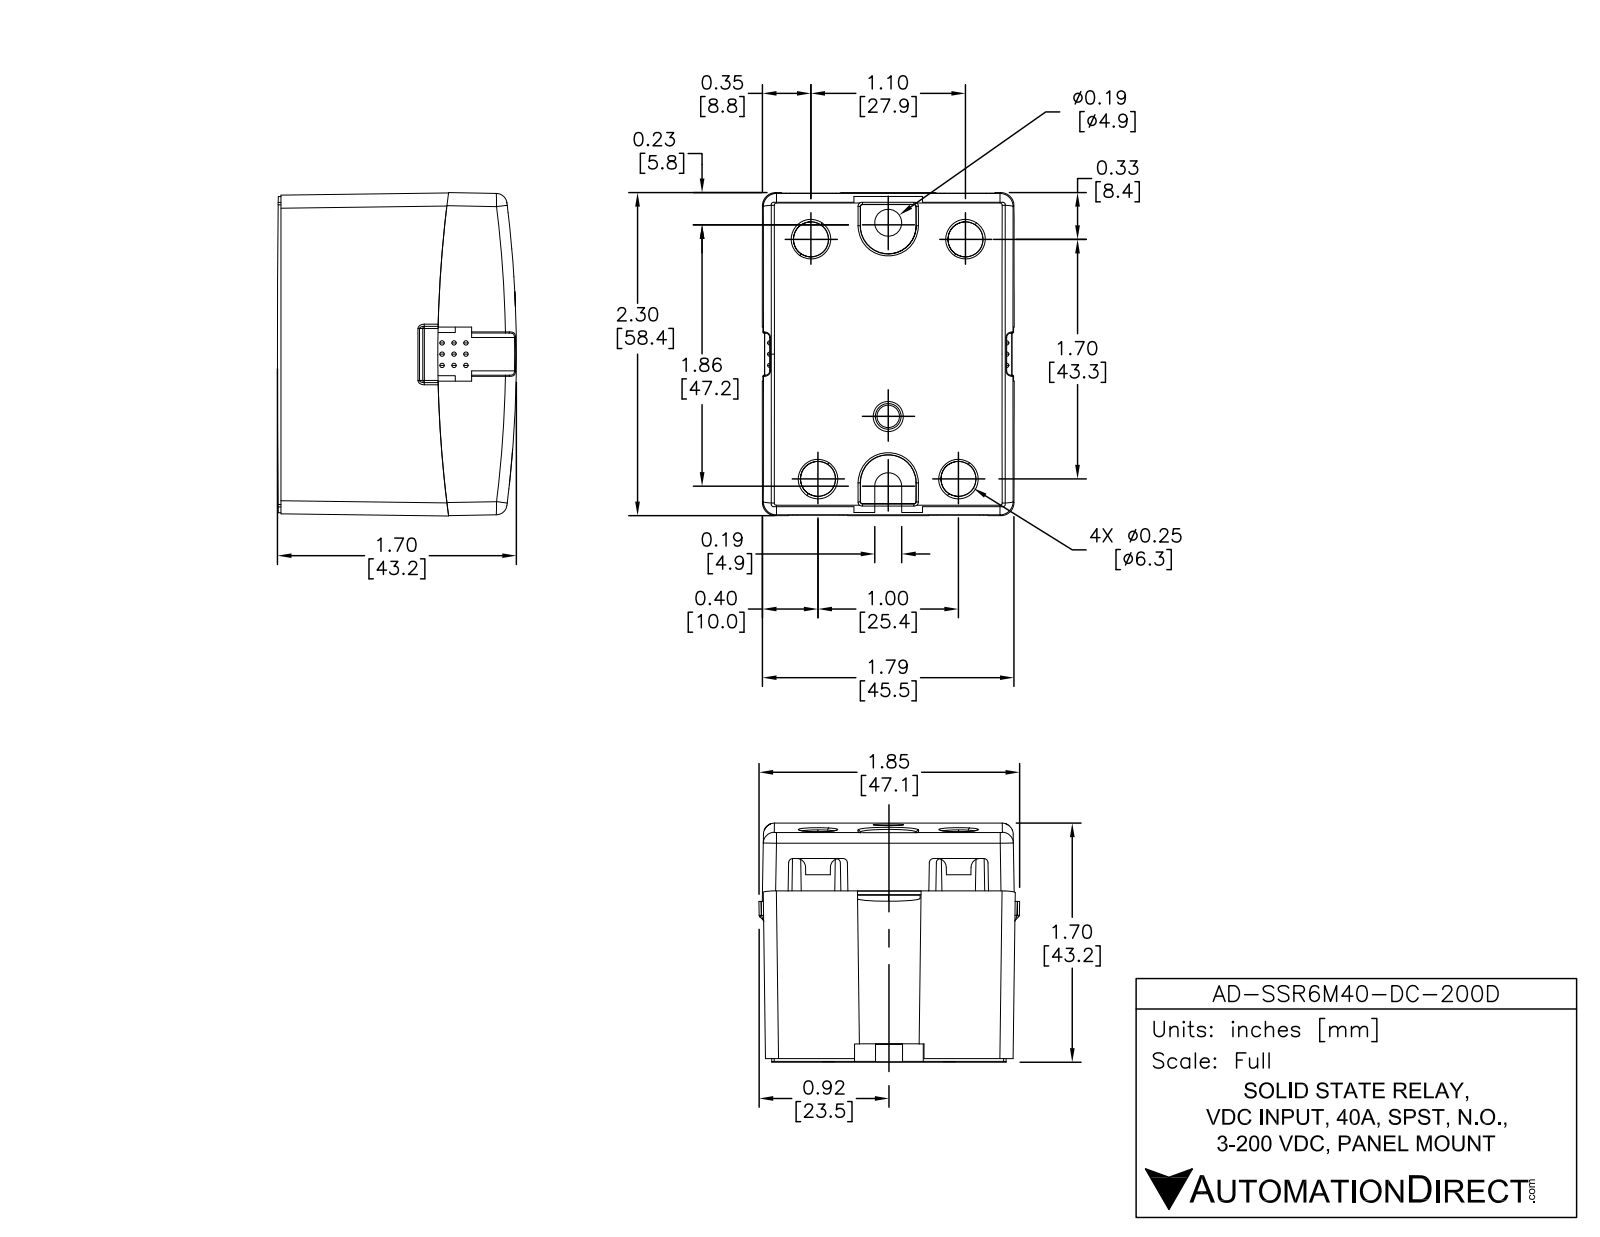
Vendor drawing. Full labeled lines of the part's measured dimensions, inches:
Part name (STEP PRODUCT): AD-SSR6M40-DC-200D
STEP written by: SolidWorks 2013 (AUTOMOTIVE_DESIGN)
Units: inches
Bodies: 1 solid, 330 faces (196 planar, 111 cylindrical, 23 other)
Overall size (bounding box): 2.3 × 1.79 × 1.7
Volume: 6.262 in³ · Surface area: 30.25 in²
Round holes (diameter × count): ⌀0.25 ×4, ⌀0.19 ×1
Round bosses / shafts (diameter × count): ⌀0.4 ×2, ⌀0.35 ×2, ⌀0.306 ×2, ⌀0.3 ×2, ⌀0.2 ×2, ⌀0.2 ×2
Partial cylindrical surfaces — rounded edges, fillets, slot ends (radius × count): R0.03 ×6, R0.01 ×4, R0.04 ×2, R0.194 ×2, R0.095 ×1, R0.498 ×1, R0.5 ×1, R0.528 ×1
Main face-to-face distances: 1.79, 2.3, 1.3, 1.05, 0.25, 0.05, 0.671, 1.059, 0.075, 2.225
Hole centre spacings: 1.1, 1.7, 2.025, 0.554, 0.564, 1.881, 1.883
